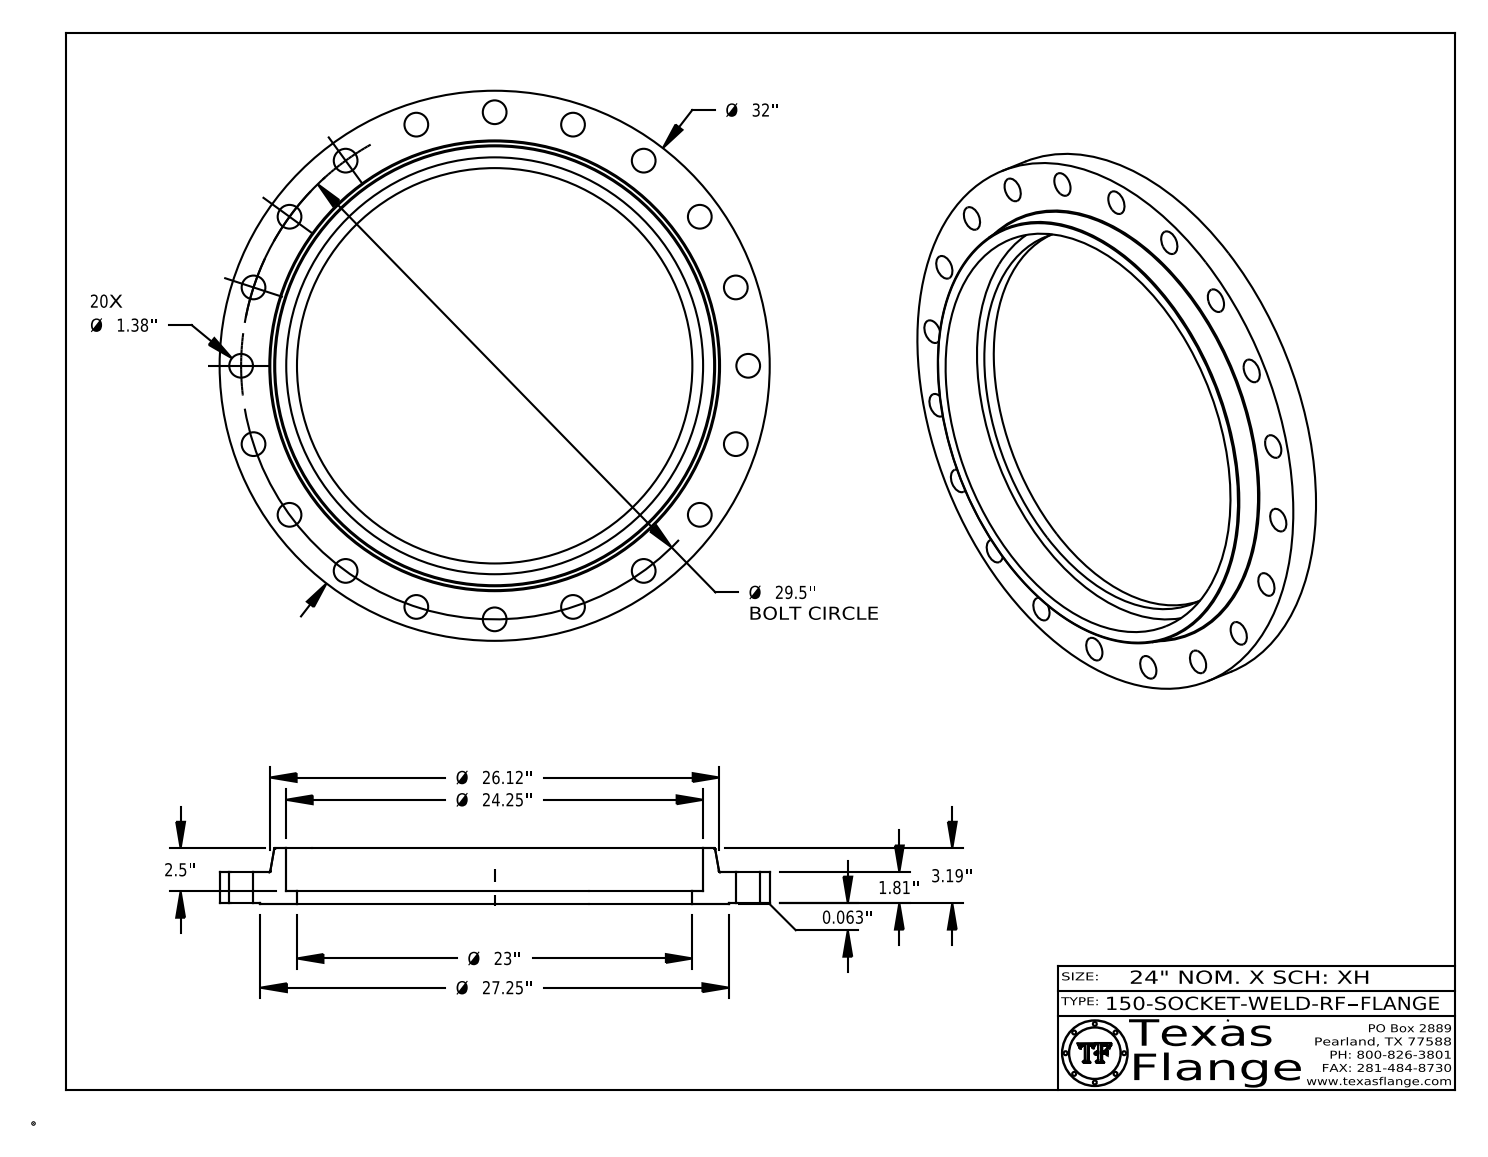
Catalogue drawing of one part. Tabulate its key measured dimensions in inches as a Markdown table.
| quantity | value |
| --- | --- |
| part name | 150-SOCKET-WELD-RF |
| STEP written by | CATIA V5 STEP AP214 (AUTOMOTIVE_DESIGN) |
| units | inches |
| bodies | 1 solid, 444 faces (370 planar, 68 cylindrical, 6 other) |
| overall size | 32 × 32 × 3.253 |
| volume | 696.5 in³ |
| surface area | 1 398 in² |
| round holes (diameter × count) | 1.38 × 20, 0.495 × 1, 23 × 1, 24.25 × 1 |
| round bosses / shafts (diameter × count) | 0.03 × 8, 32 × 1, 27.25 × 1, 0.39 × 1 |
| main face-to-face distances | 1.81, 0.063, 1.872, 3.253, 3.19, 1.38, 0.753, 0.69, 1.12, 2.5 |
| hole center spacings | 14.75, 29.137, 4.615, 17.34, 20.859, 23.866, 26.285, 9.116 |
